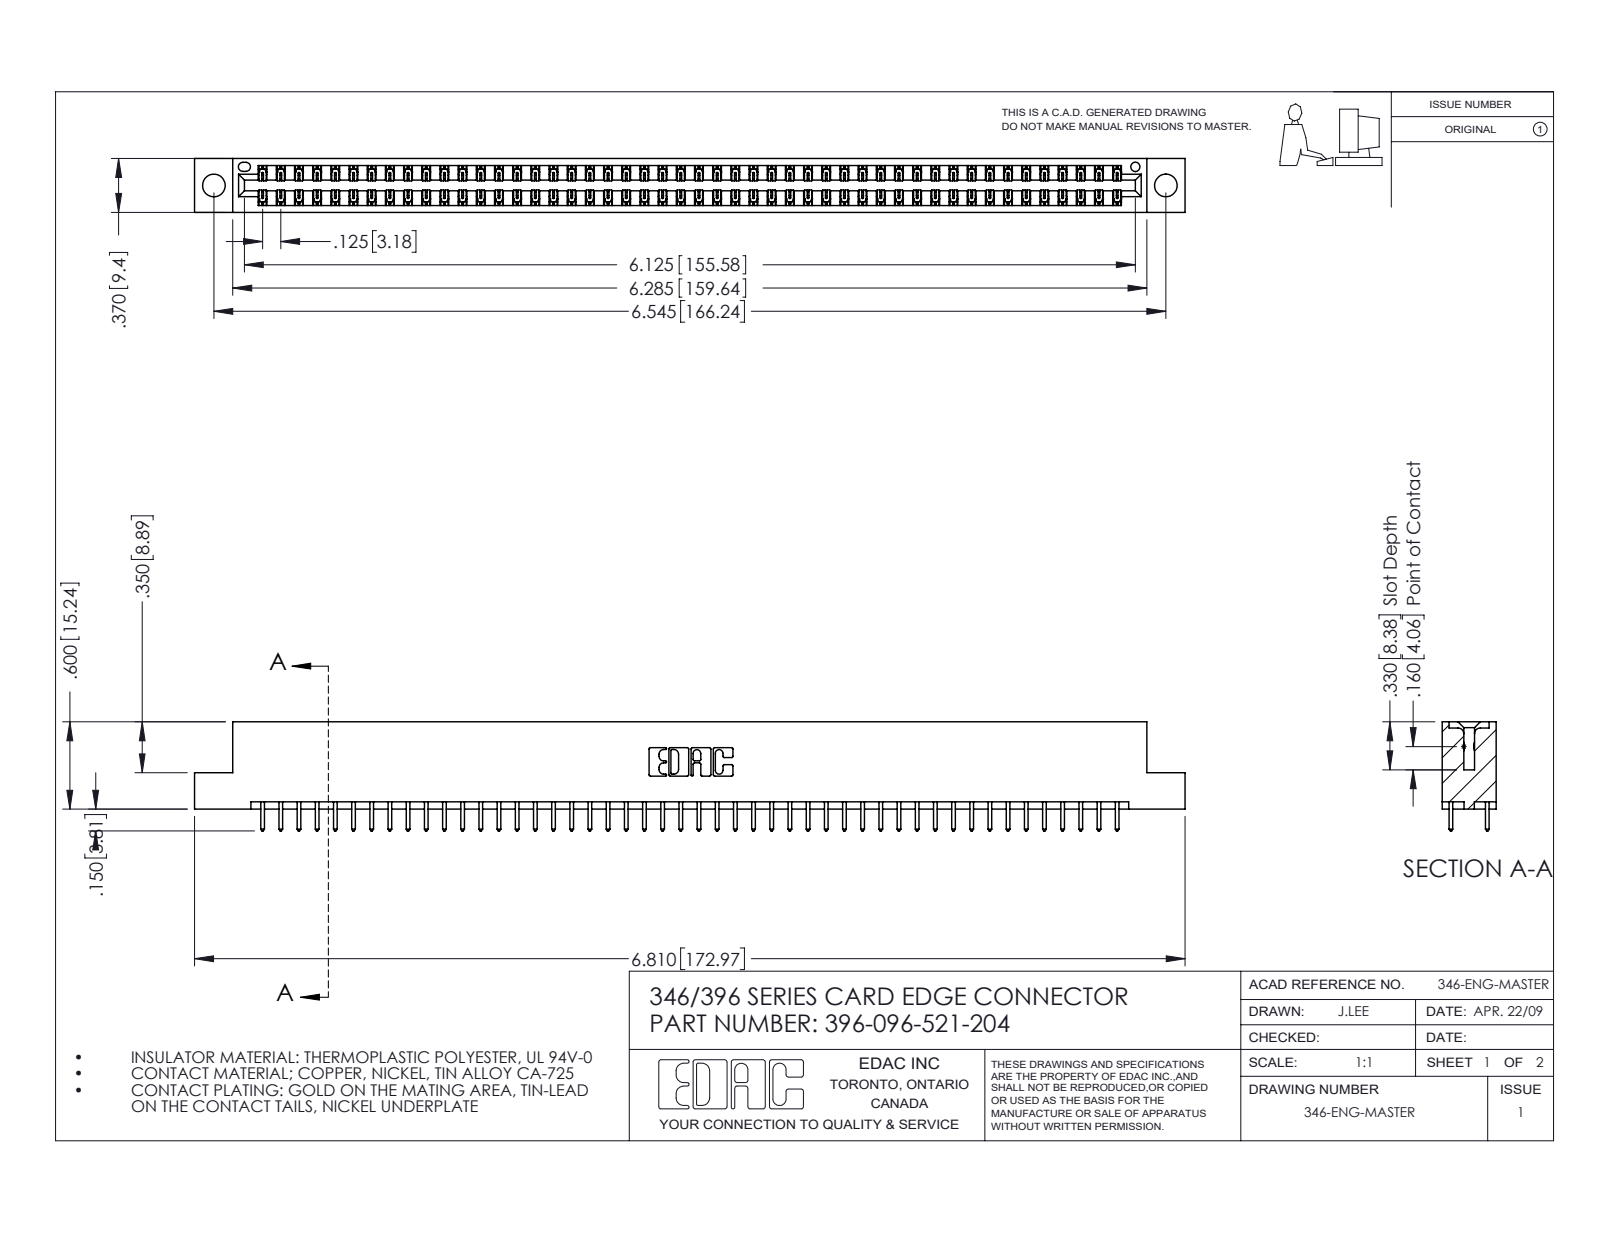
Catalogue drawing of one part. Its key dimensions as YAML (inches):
part_name: "345-292-001_345-293-121; 396-096-521-204; 346 Part_Flush Mounting Lugs - 0.156 Dia-TH"
step_written_by: "SolidWorks 2016 (CONFIG_CONTROL_DESIGN)"
units: inches
bodies: {solids: 97, faces: 5114, planar: 3436, cylindrical: 1678, other: 0}
overall_size: [6.81, 0.75, 0.37]
volume: 1.024
surface_area: 35.21
round_holes:
  - {diameter: 0.156, count: 2}
  - {diameter: 0.064, count: 1}
partial_cylinders:
  - {radius: 0.006, count: 144}
  - {radius: 0.01, count: 96}
  - {radius: 0.01, count: 22}
  - {radius: 0.007, count: 6}
  - {radius: 0.031, count: 6}
  - {radius: 0.026, count: 3}
  - {radius: 0.014, count: 2}
  - {radius: 0.022, count: 2}
face_to_face_distances: [0.048, 0.322, 0.25, 0.37, 0.072, 0.298, 0.025, 0.275, 0.148, 0.222]
hole_center_spacings: [0.246, 6.336, 6.545]
